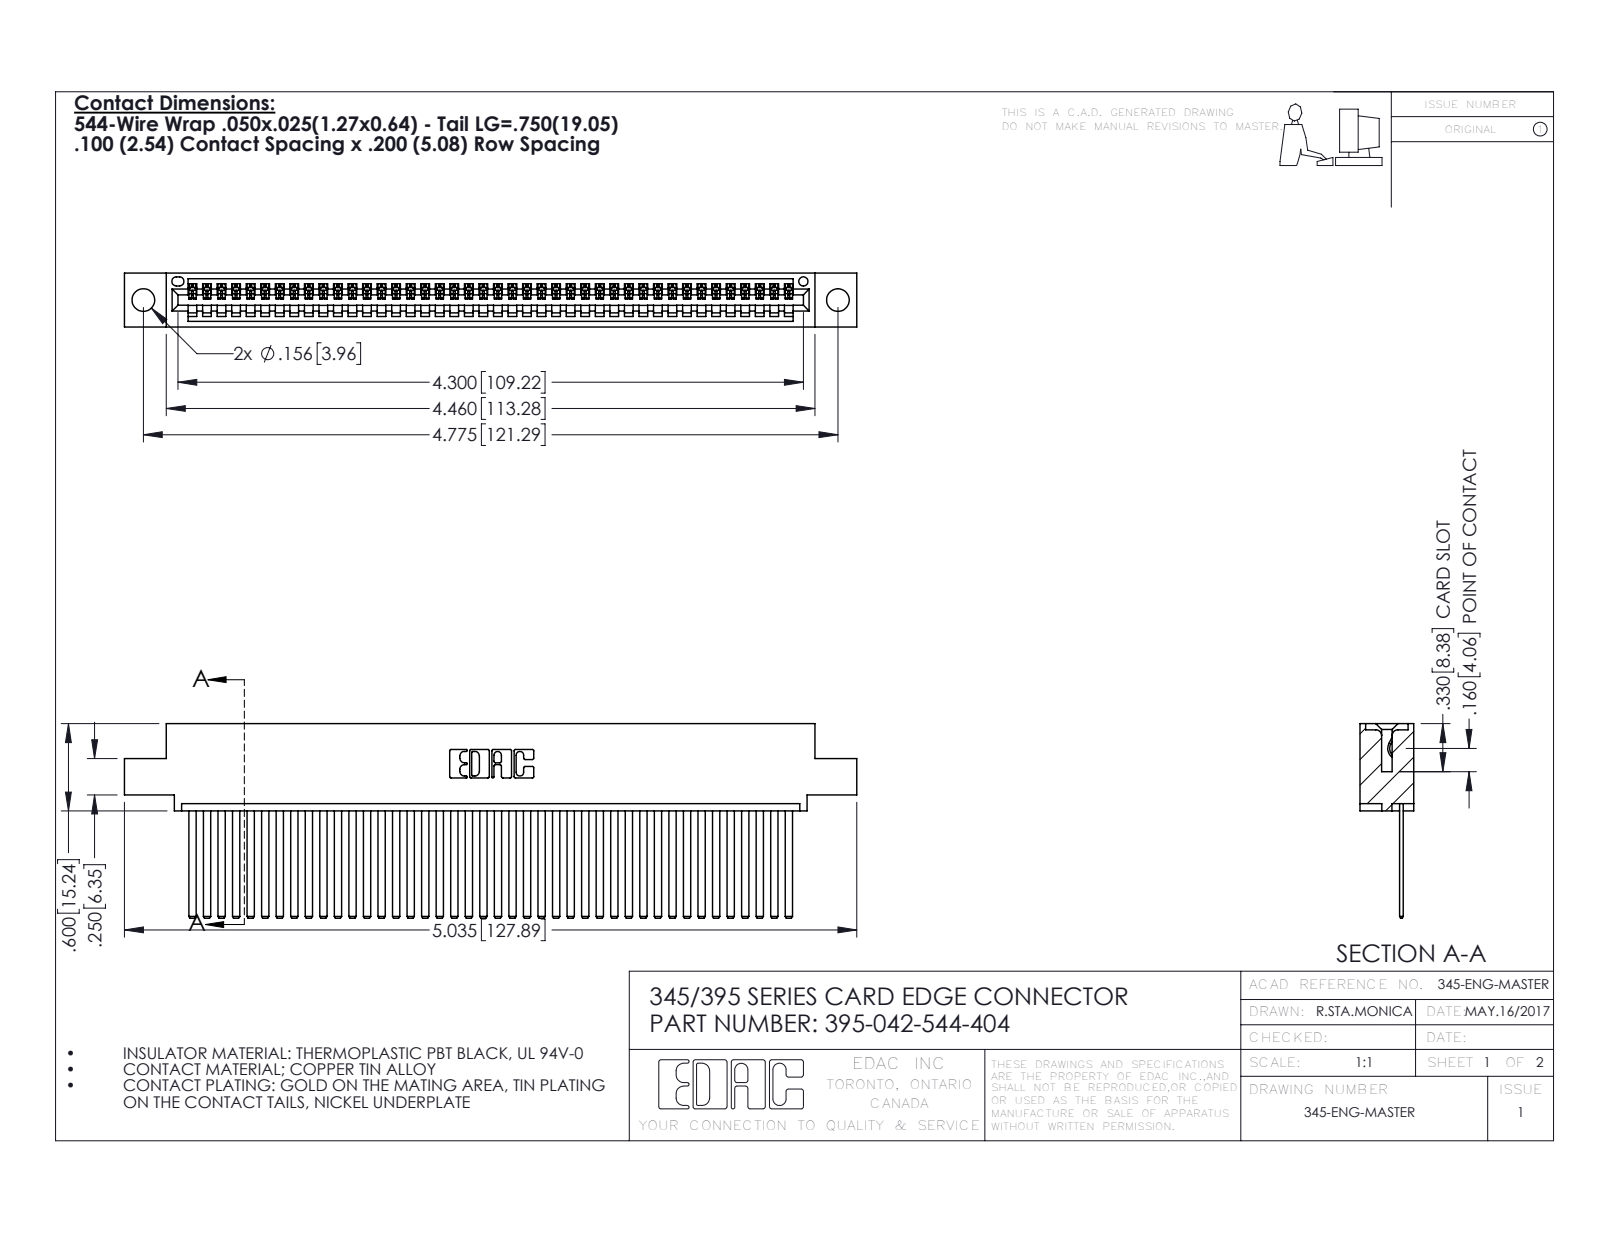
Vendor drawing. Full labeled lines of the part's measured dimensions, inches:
Part name (STEP PRODUCT): 345 Part_0.110 Offset - 0.156 Dia-TH; 395-042-544-404; 345-292-001_345-293-144
STEP written by: SolidWorks 2016 (CONFIG_CONTROL_DESIGN)
Units: inches
Bodies: 43 solids, 2314 faces (1596 planar, 718 cylindrical, 0 other)
Overall size (bounding box): 5.035 × 1.337 × 0.37
Volume: 0.761 in³ · Surface area: 27.78 in²
Round holes (diameter × count): ⌀0.156 ×2, ⌀0.064 ×1
Partial cylindrical surfaces — rounded edges, fillets, slot ends (radius × count): R0.006 ×84, R0.01 ×22, R0.007 ×6, R0.031 ×6, R0.026 ×3, R0.031 ×2, R0.04 ×2, R0.014 ×1
Main face-to-face distances: 0.072, 0.298, 0.025, 0.098, 0.272, 0.37, 0.2, 0.225, 0.149, 0.072
Hole centre spacings: 0.27, 4.539, 4.775
